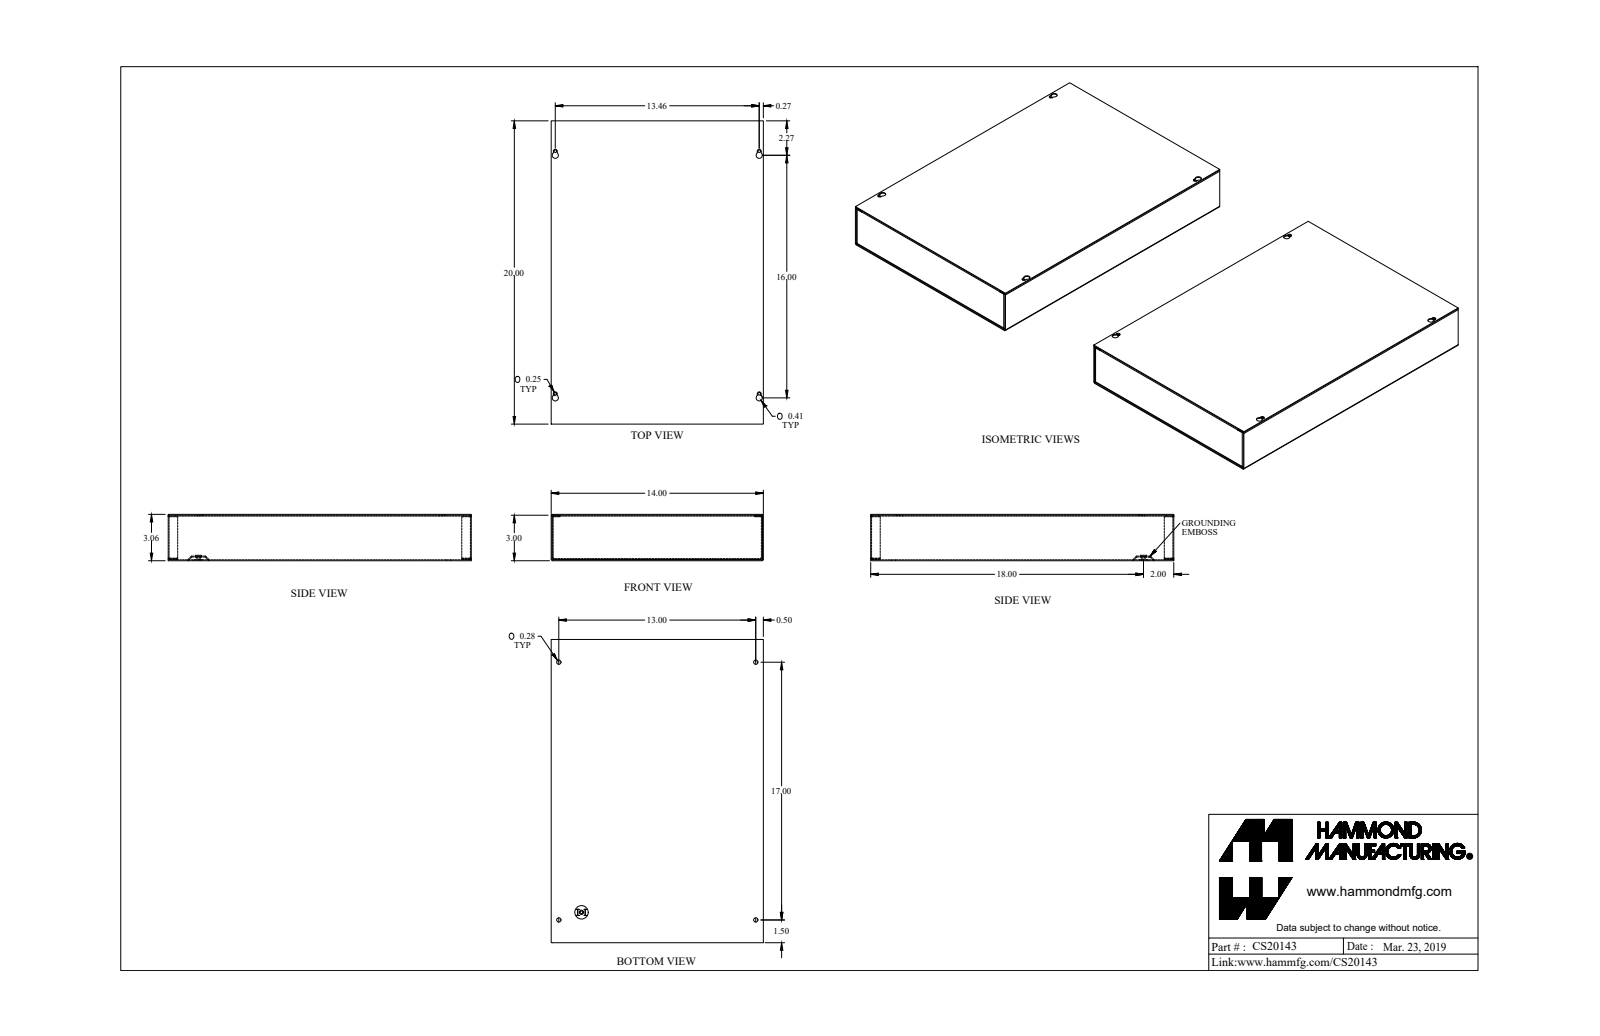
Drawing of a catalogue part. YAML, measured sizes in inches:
part_name: "CS20143_Default"
step_written_by: "SolidWorks 2019 (CONFIG_CONTROL_DESIGN)"
units: inches
bodies: {solids: 4, faces: 205, planar: 125, cylindrical: 72, other: 8}
overall_size: [20, 14, 3.057]
volume: 45.89
surface_area: 1624
round_holes:
  - {diameter: 0.17, count: 5}
  - {diameter: 0.281, count: 4}
  - {diameter: 0.5, count: 1}
round_bosses_or_shafts:
  - {diameter: 0.492, count: 1}
  - {diameter: 0.284, count: 1}
partial_cylinders:
  - {radius: 0.029, count: 12}
  - {radius: 0.086, count: 12}
  - {radius: 0.057, count: 8}
  - {radius: 0.125, count: 4}
  - {radius: 0.203, count: 4}
face_to_face_distances: [0.057, 3, 2.943, 3.057, 13.943, 19.943, 14, 13.886, 20, 19.886]
hole_center_spacings: [0.55, 13.239, 16.502, 21.149, 13, 13.46, 16, 17]
